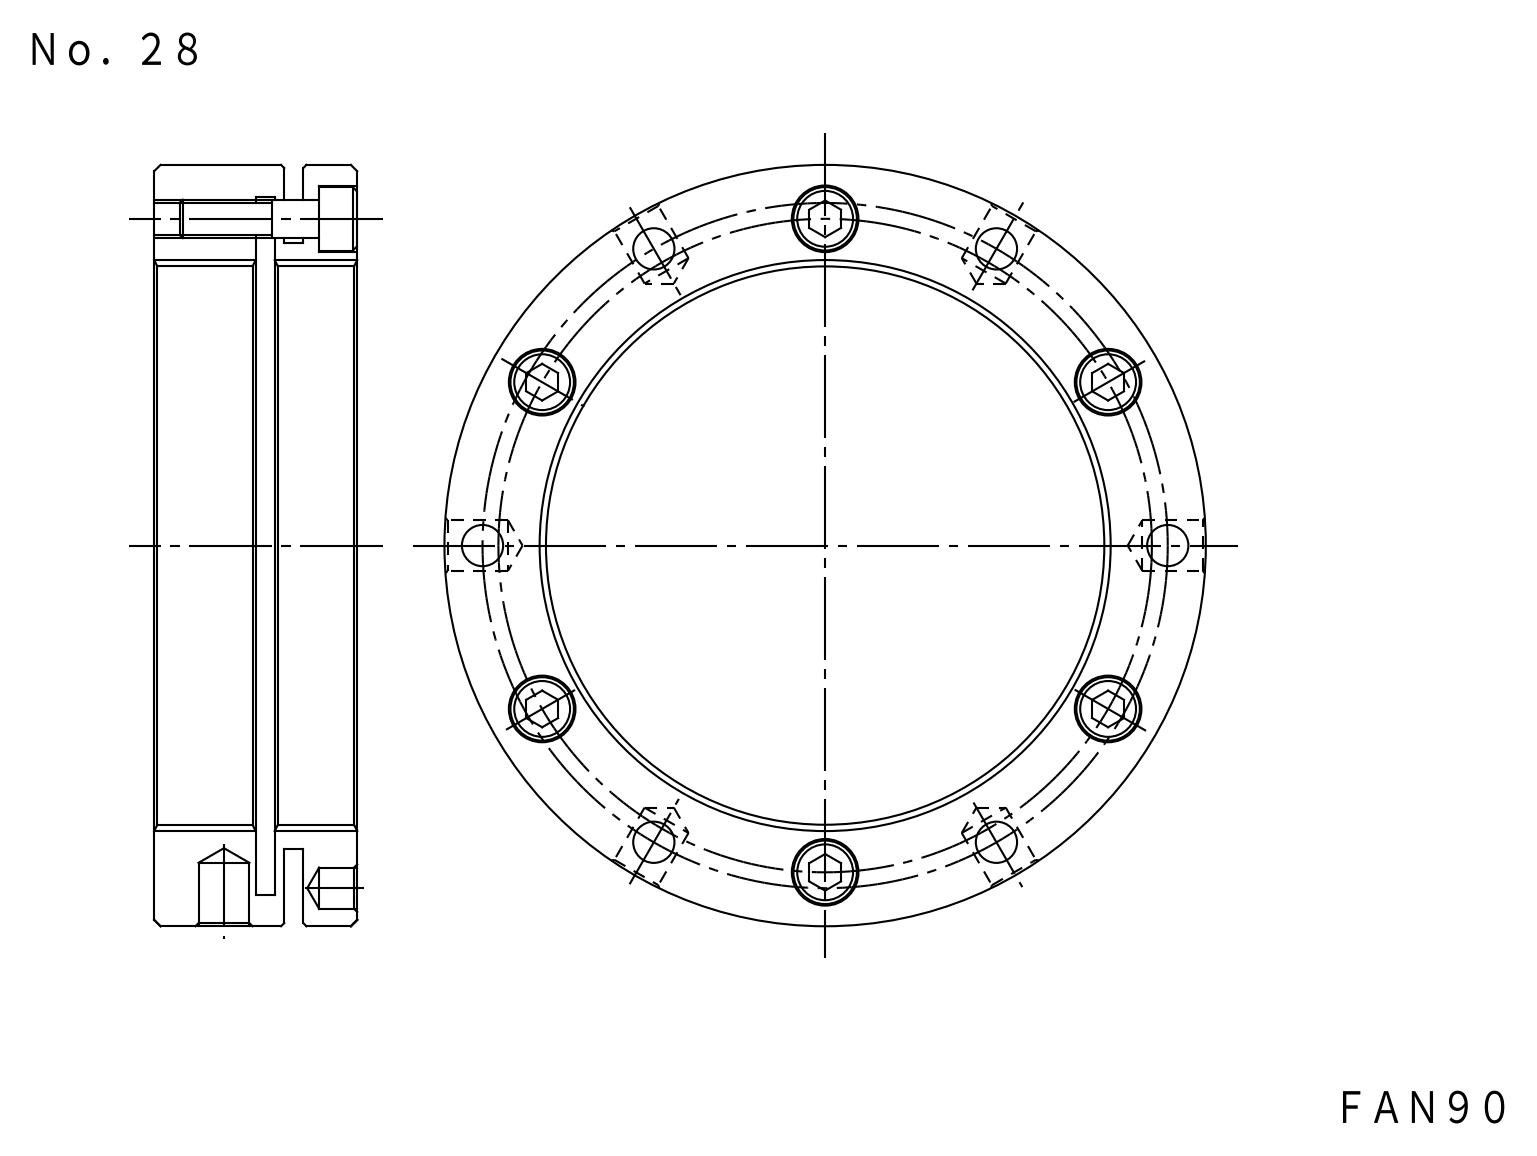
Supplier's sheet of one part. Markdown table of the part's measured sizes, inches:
| quantity | value |
| --- | --- |
| part name | FKD FAN90; M6X22_default |
| STEP written by | SolidWorks 2012 (CONFIG_CONTROL_DESIGN) |
| units | inches |
| bodies | 7 solids, 204 faces (72 planar, 108 cylindrical, 24 other) |
| overall size | 4.724 × 4.724 × 1.26 |
| volume | 8.338 in³ |
| surface area | 84.66 in² |
| round holes (diameter × count) | 0.248 × 6, 0.256 × 6, 0.413 × 6, 0.194 × 3, 0.194 × 3, 0.315 × 3, 3.543 × 1, 4.449 × 1 |
| round bosses / shafts (diameter × count) | 0.394 × 6, 0.236 × 6, 4.724 × 1, 3.898 × 1 |
| main face-to-face distances | 0.098, 0.157, 1.26, 0.669, 0.591, 0.768, 0.492, 0.827, 0.059, 0.433 |
| hole center spacings | 1.091, 2.087, 2.126, 4.069, 2.979, 3.614, 2.979, 3.682 |
